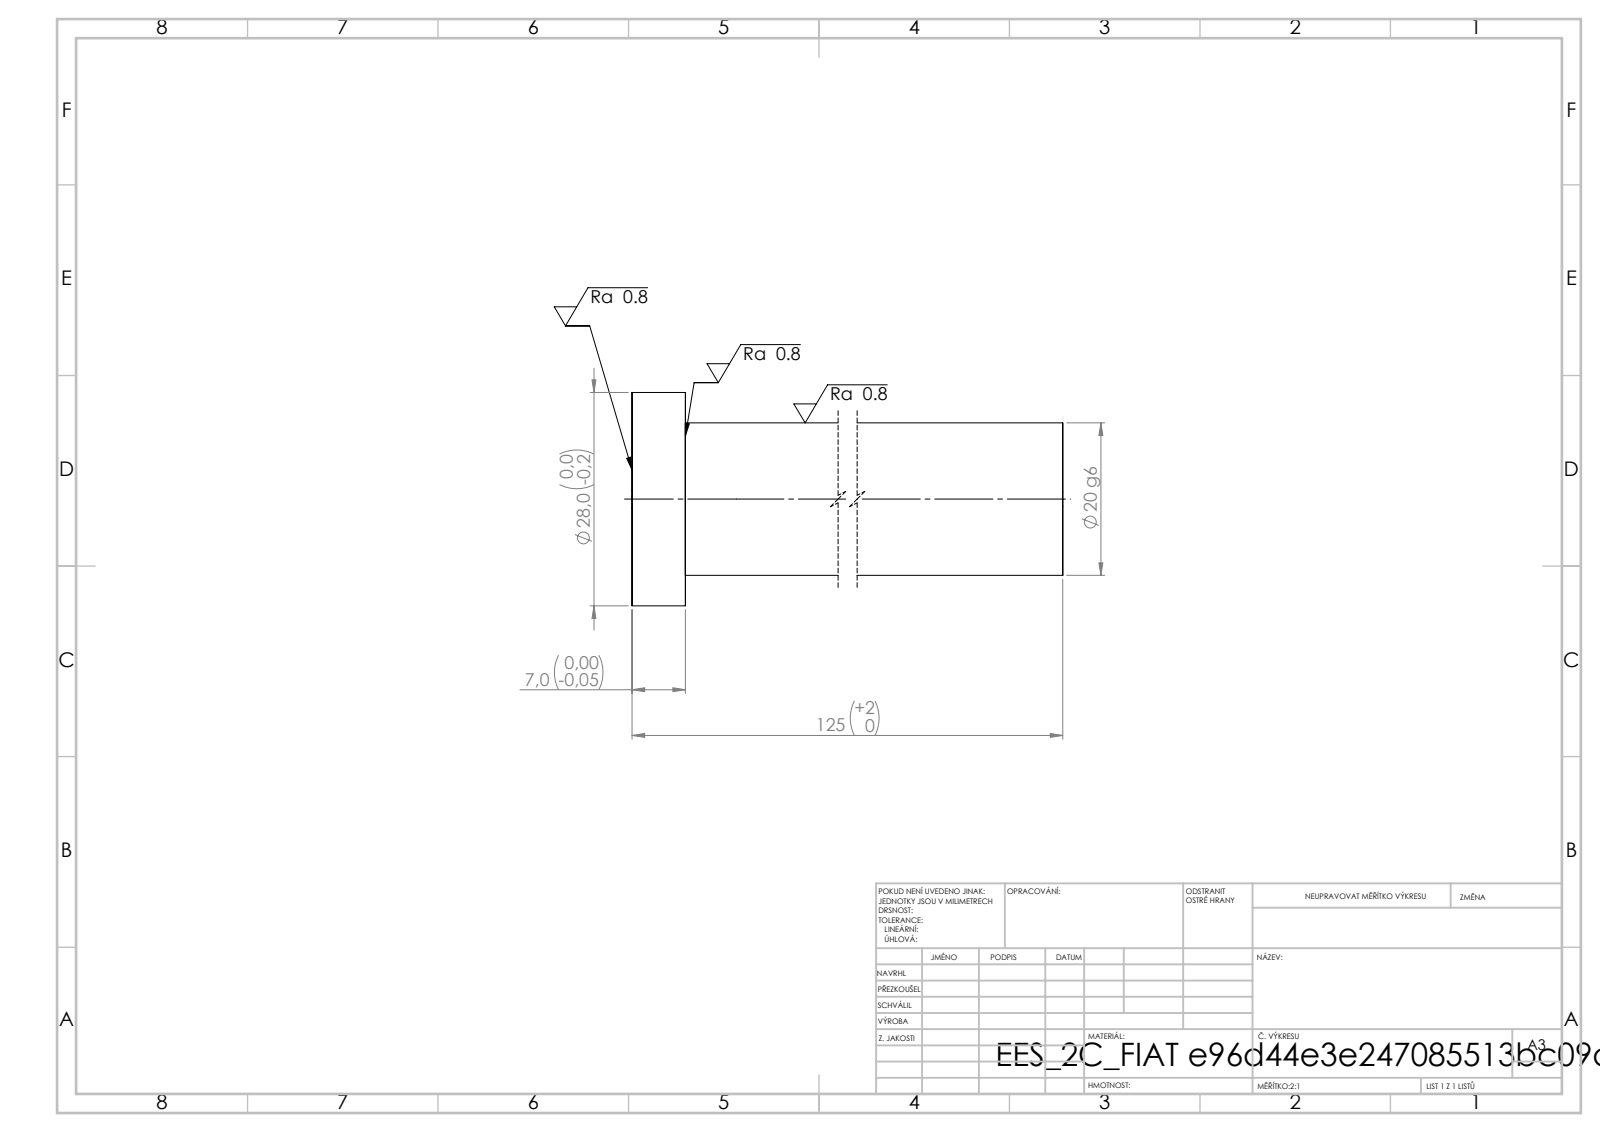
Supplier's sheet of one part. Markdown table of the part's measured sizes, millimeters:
| quantity | value |
| --- | --- |
| STEP written by | SolidWorks 2019 (CONFIG_CONTROL_DESIGN) |
| units | millimeters |
| bodies | 1 solid, 7 faces (3 planar, 4 cylindrical, 0 other) |
| overall size | 125 × 28 × 28 |
| volume | 41 381 mm³ |
| surface area | 9 261 mm² |
| round bosses / shafts (diameter × count) | 28 × 1, 20 × 1 |
| main face-to-face distances | 125, 7, 118 |
